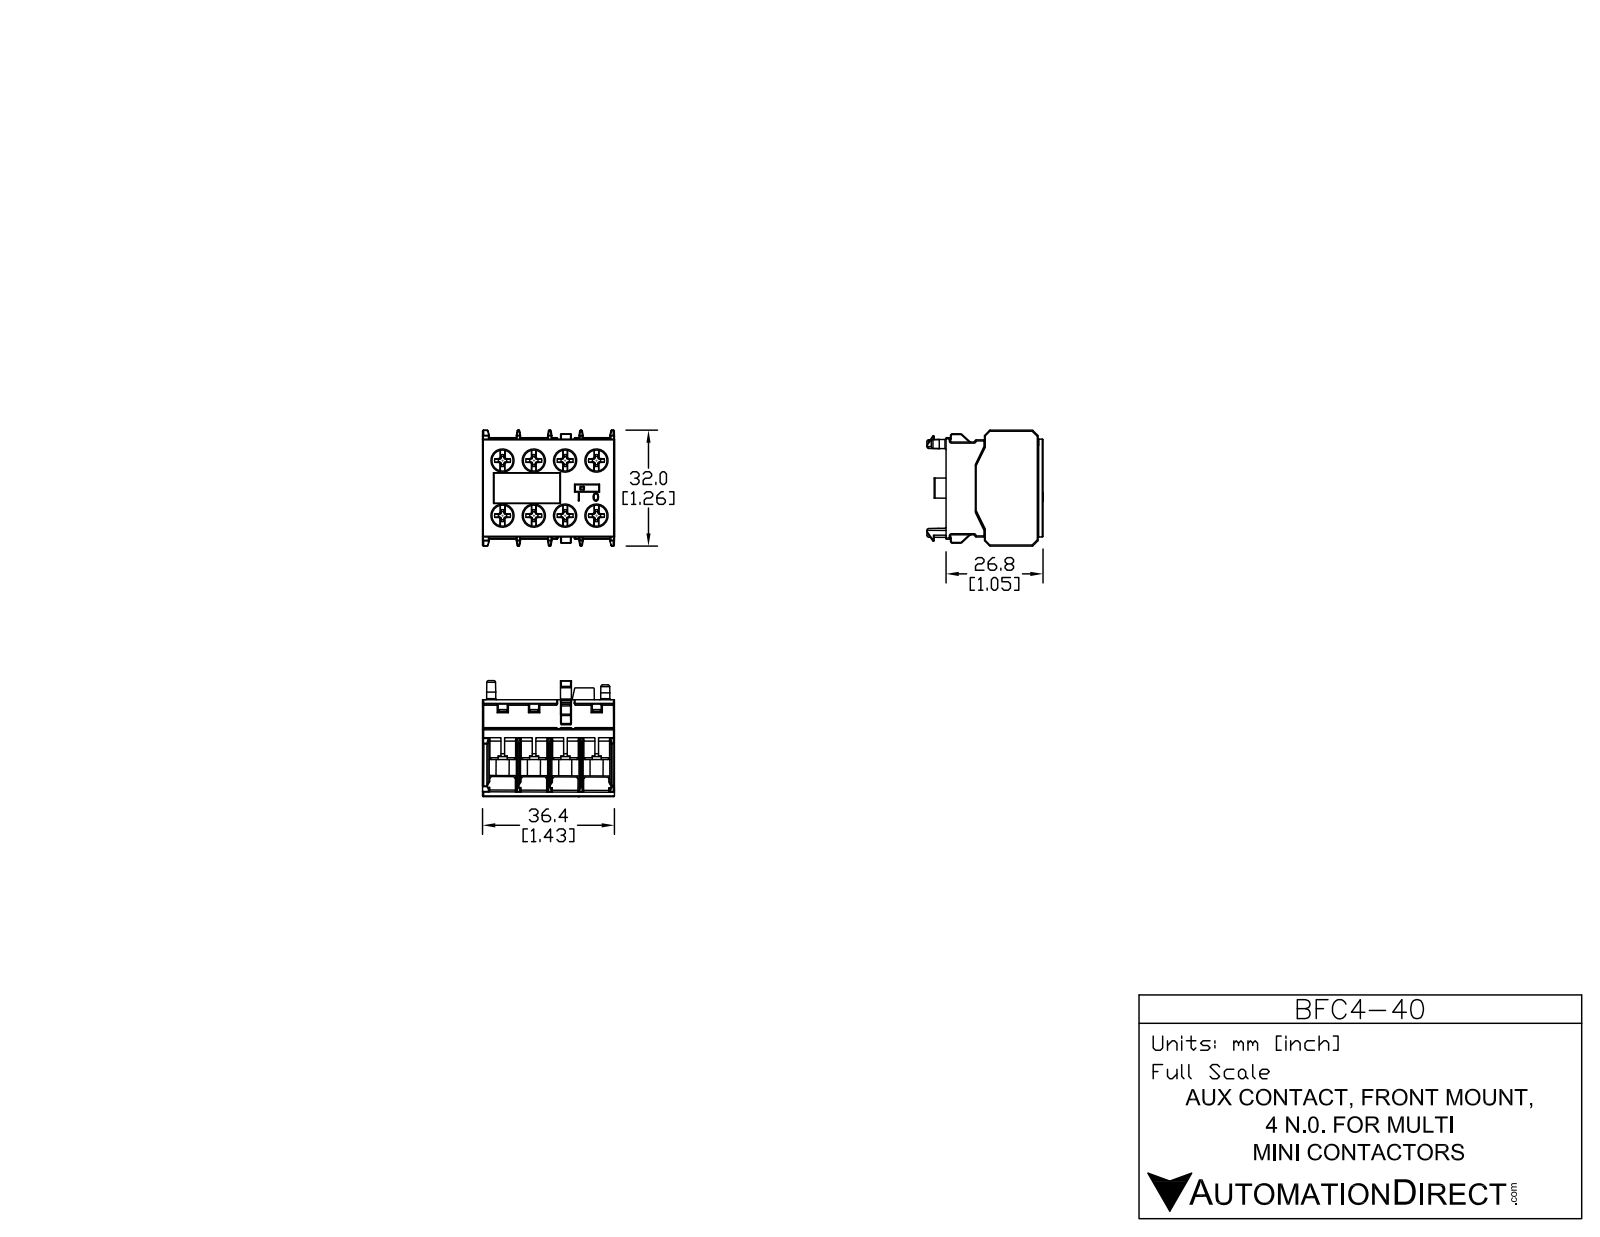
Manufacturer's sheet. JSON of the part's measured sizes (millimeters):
{"part_name": "BFC4-40", "step_written_by": "SolidWorks 2013 (AUTOMOTIVE_DESIGN)", "units": "millimeters", "bodies": {"solids": 20, "faces": 761, "planar": 593, "cylindrical": 168, "other": 0}, "overall_size": [36.5, 32.23, 32], "volume_mm3": 16423, "surface_area_mm2": 17387, "round_holes": [[6, 8]], "round_bosses_or_shafts": [[5, 8], [3, 8], [2.75, 3]], "partial_cylinders_radius": [[0.5, 8], [4.52, 8], [0.3, 6], [0.25, 4], [0.14, 2], [0.19, 2], [0.2, 2]], "face_to_face_distances": [1.25, 17.25, 8.63, 16, 8.62, 25.88, 7.38, 18.5, 9.88, 7.37], "hole_center_spacings": [8.63, 15, 17.25, 17.31, 22.86, 8.62, 17.3, 25.88]}
